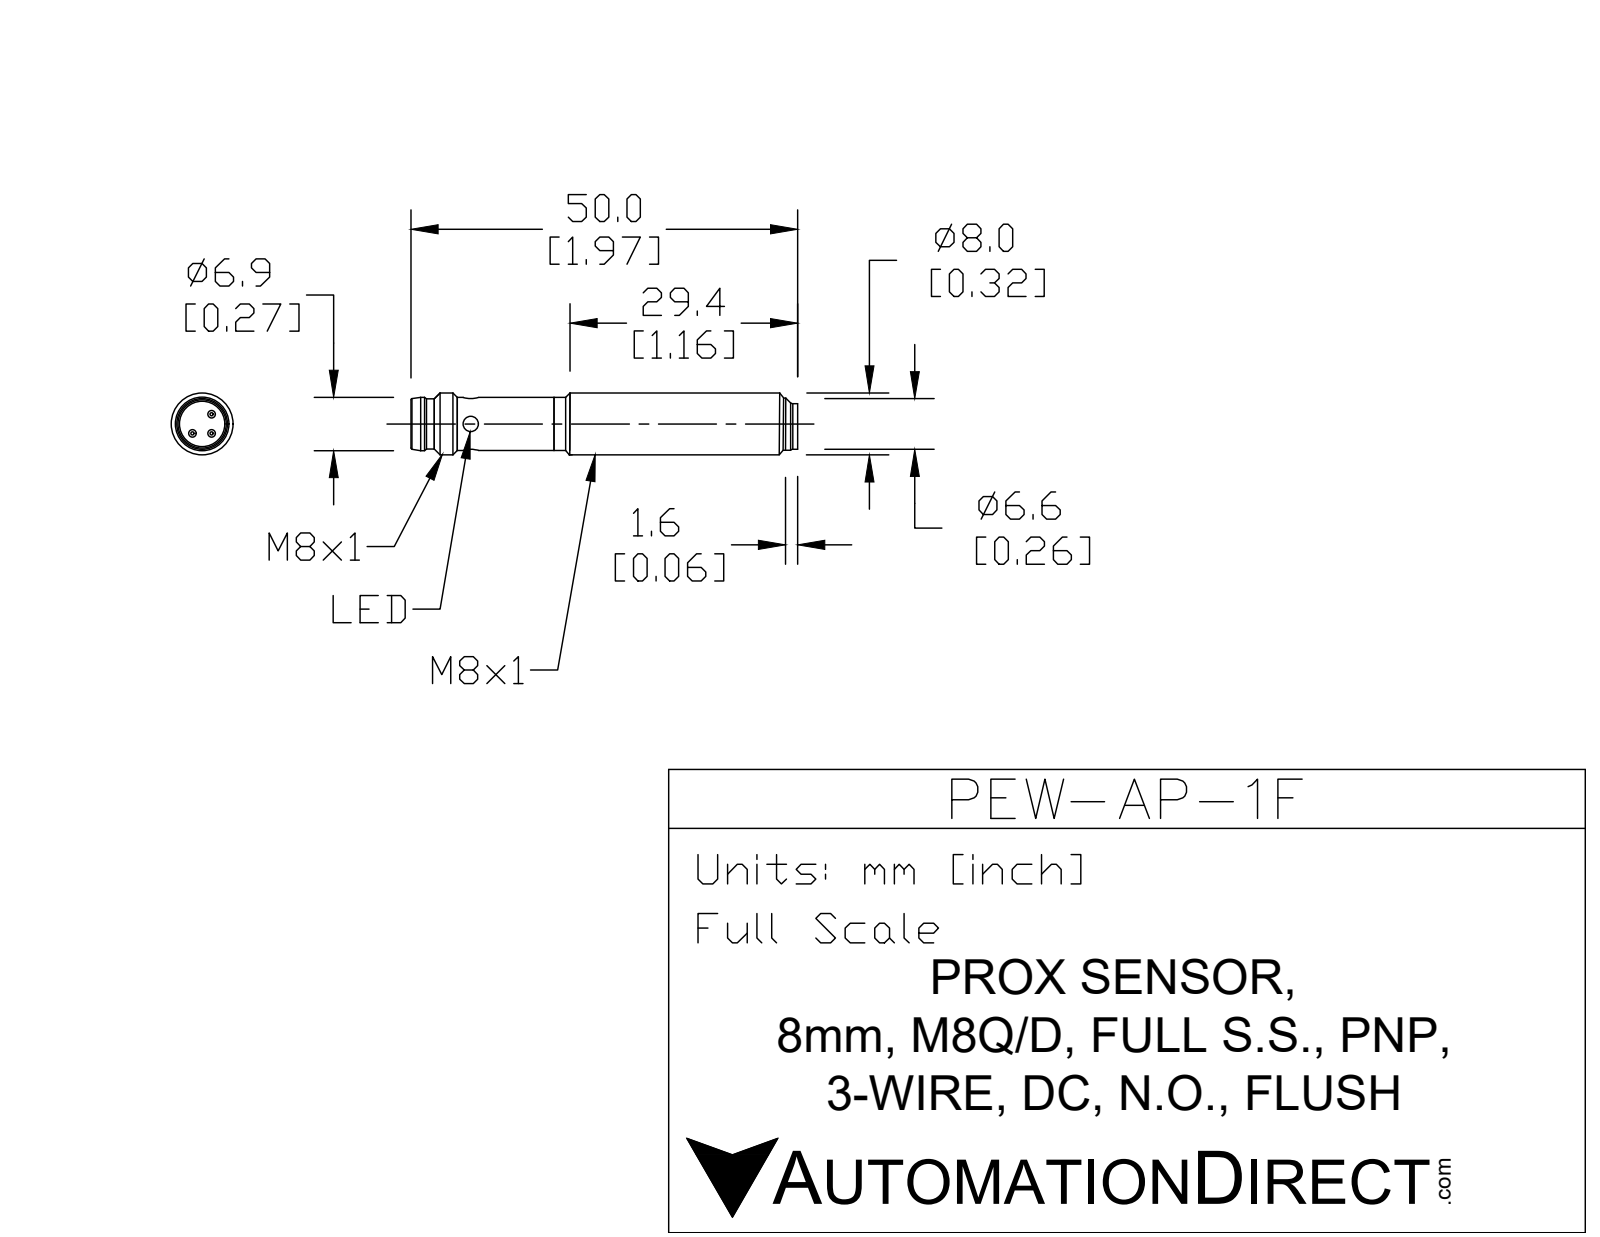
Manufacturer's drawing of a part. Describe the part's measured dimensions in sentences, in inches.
The part is named "PEW-AP-1F". Its 3-D file was written by "SolidWorks 2017 (AUTOMOTIVE_DESIGN)". It is 3 solids with 103 faces: 23 planar, 26 cylindrical and 54 other. Overall it measures 1.969 by 0.591 by 0.512 inches. Its volume is 0.18 cubic inches and its surface area 3.602 square inches. Round holes: 2 of diameter 0.079, 1 of diameter 0.23, 1 of diameter 0.272. Round bosses or shafts: 1 of diameter 0.315, 1 of diameter 0.272, 1 of diameter 0.27, 1 of diameter 0.258, 1 of diameter 0.256. The main face-to-face distances are 0.512, 0.157, 0.315, 0.787, 0.63, 0.472, 0.984, 1.142, 1.299, 1.772.
